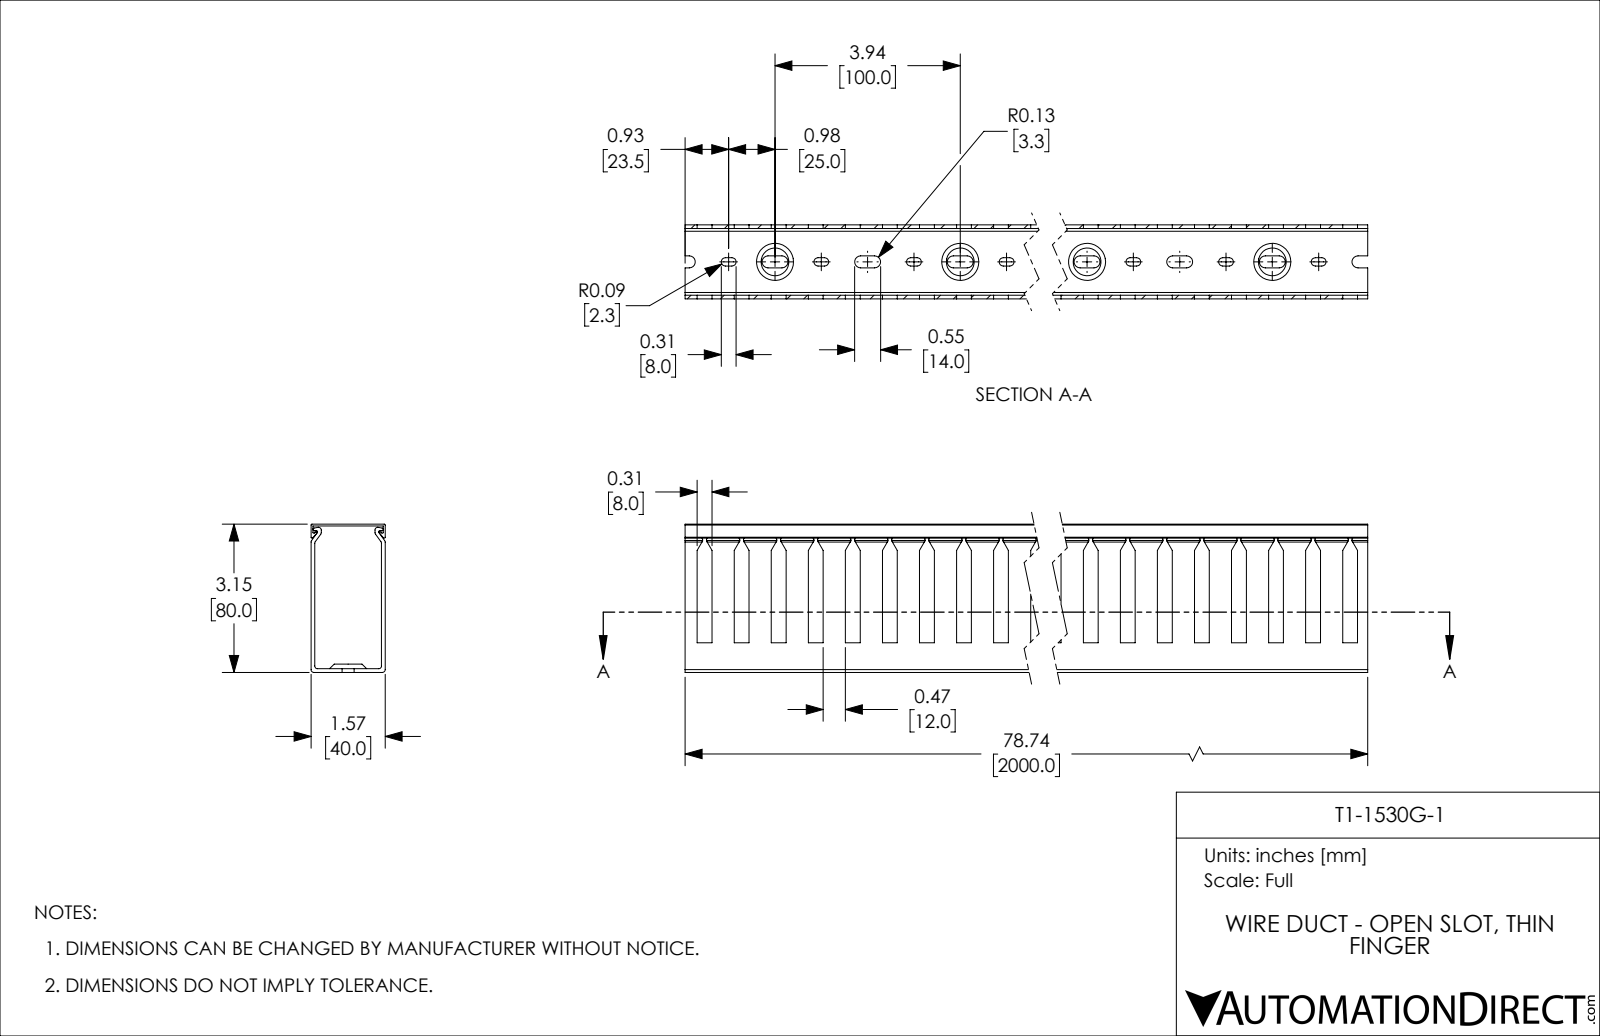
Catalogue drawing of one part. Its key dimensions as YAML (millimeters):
part_name: "T1-1530G-1"
step_written_by: "SolidWorks 2021 (CONFIG_CONTROL_DESIGN)"
units: millimeters
bodies: {solids: 2, faces: 1005, planar: 534, cylindrical: 431, other: 40}
overall_size: [2000, 80, 40]
volume: 890552
surface_area: 1009000
partial_cylinders:
  - {radius: 2.25, count: 80}
  - {radius: 3.25, count: 80}
  - {radius: 1.5, count: 12}
  - {radius: 0.5, count: 8}
  - {radius: 0.75, count: 6}
face_to_face_distances: [2, 38, 40, 36, 1, 80, 79, 77, 78, 39]
